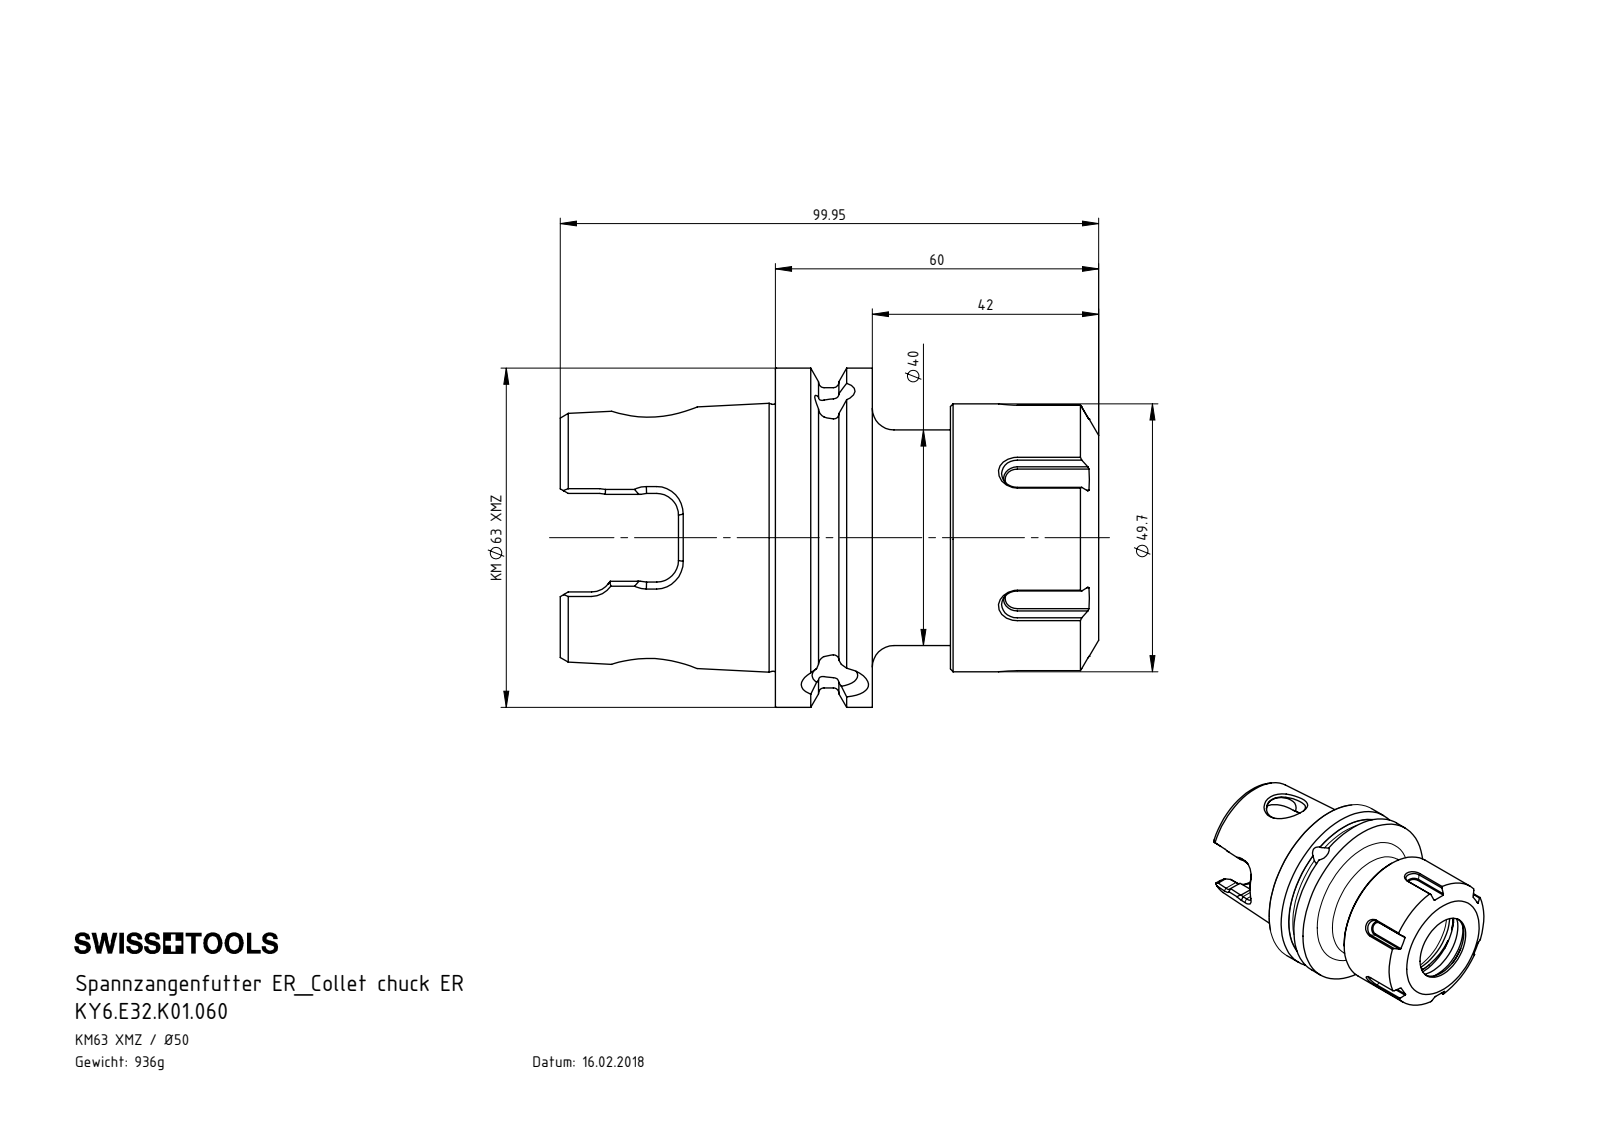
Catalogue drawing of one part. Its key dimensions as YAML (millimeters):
part_name: "KY6.E32.K01.060; E32-ER1.002.027; KY6-E32.K01.060_A"
step_written_by: "SolidWorks 2017 (CONFIG_CONTROL_DESIGN)"
units: millimeters
bodies: {solids: 2, faces: 317, planar: 100, cylindrical: 70, other: 147}
overall_size: [99.95, 62.95, 62.95]
volume: 119176
surface_area: 36171
round_holes:
  - {diameter: 7.47, count: 2}
  - {diameter: 7, count: 1}
  - {diameter: 8.48, count: 1}
  - {diameter: 10, count: 1}
  - {diameter: 11.5, count: 1}
  - {diameter: 14.5, count: 1}
  - {diameter: 23.5, count: 1}
  - {diameter: 24, count: 1}
  - {diameter: 27.1, count: 1}
  - {diameter: 29.5, count: 1}
  - {diameter: 31.1, count: 1}
  - {diameter: 35.27, count: 1}
round_bosses_or_shafts:
  - {diameter: 62.95, count: 1}
  - {diameter: 55.7, count: 1}
  - {diameter: 49.7, count: 1}
  - {diameter: 40, count: 1}
partial_cylinders:
  - {radius: 4, count: 6}
  - {radius: 7.04, count: 2}
  - {radius: 15.5, count: 2}
face_to_face_distances: [14.5, 18, 32.5, 60, 42, 27.5, 1.1, 19.1, 33.6, 61.1]
